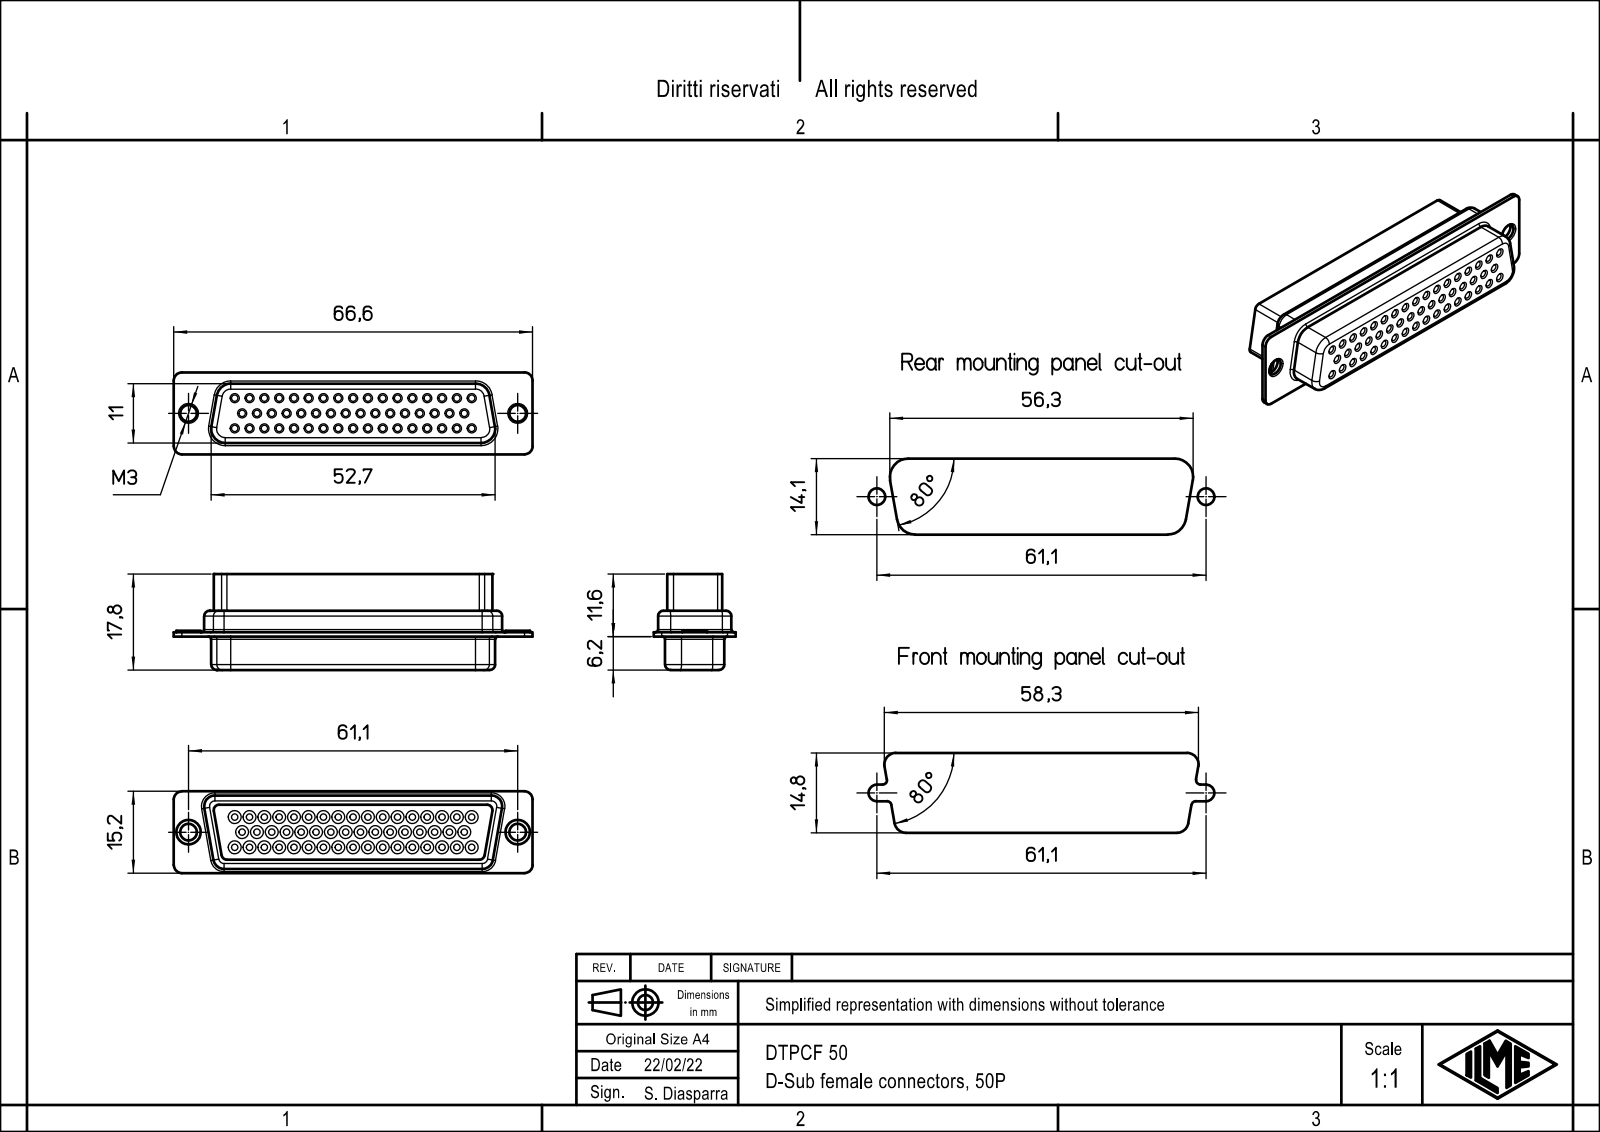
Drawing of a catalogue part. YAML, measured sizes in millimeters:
part_name: "DPTCF_50"
step_written_by: "Creo Elements/Direct Modeling 20.1B 02-Apr-2019 (C) Parametric Technology GmbH (AUTOMOTIVE_DESIGN)"
units: millimeters
bodies: {solids: 1, faces: 433, planar: 73, cylindrical: 240, other: 120}
overall_size: [66.6, 17.8, 15.2]
volume: 7626
surface_area: 9515
round_holes:
  - {diameter: 1.2, count: 50}
  - {diameter: 2.4, count: 50}
  - {diameter: 3.1, count: 2}
round_bosses_or_shafts:
  - {diameter: 4.55, count: 2}
partial_cylinders:
  - {radius: 1, count: 12}
  - {radius: 0.5, count: 8}
  - {radius: 1.5, count: 4}
  - {radius: 2, count: 4}
  - {radius: 2.6, count: 4}
face_to_face_distances: [0.4, 10.6, 6.2, 10.2, 11, 0.8, 11.6, 17.8, 1.3, 1.7]
hole_center_spacings: [3.12, 2.75, 5.5, 8.25, 4.99, 11, 6.24, 16.5]
